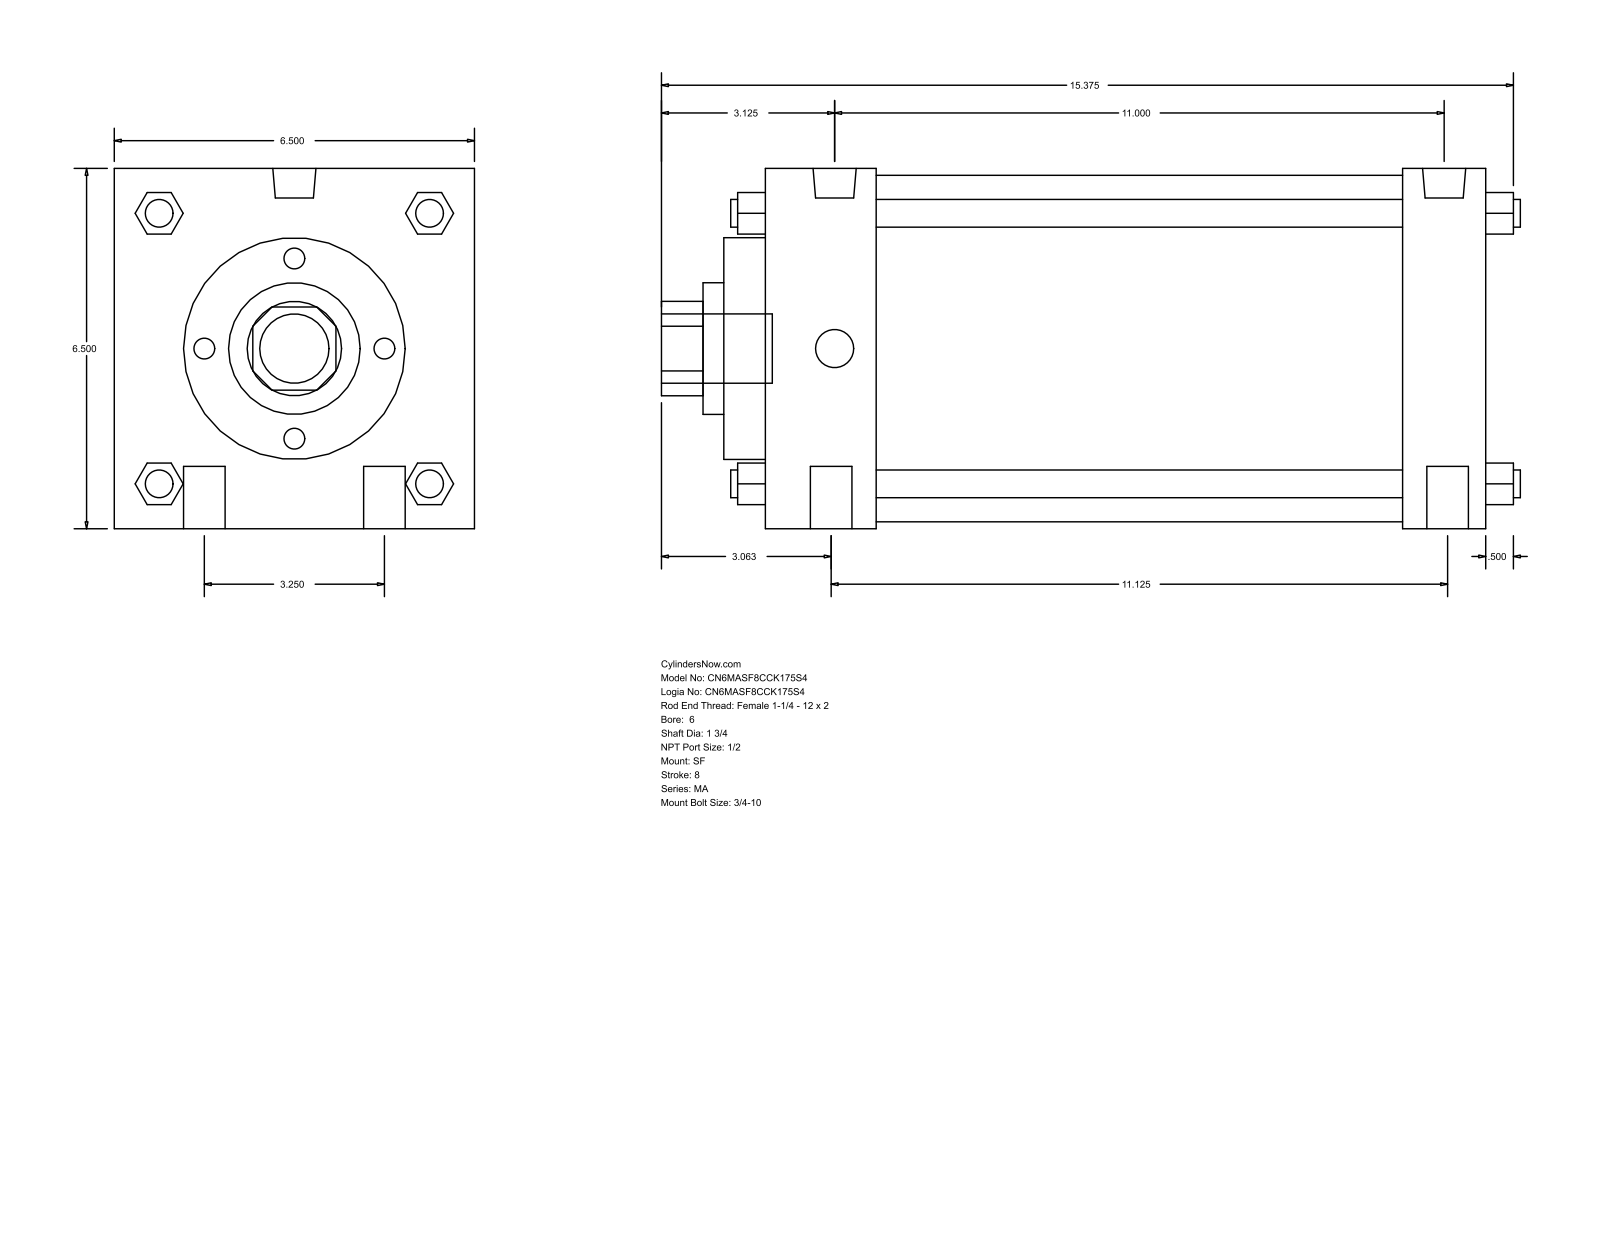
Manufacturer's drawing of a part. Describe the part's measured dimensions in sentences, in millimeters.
The part is named "MA_SF__0600_1.75". Its 3-D file was written by "GSSL Pune (CONFIG_CONTROL_DESIGN)". It is 0 solids with 126 faces: 95 planar, 31 cylindrical and 0 other. Overall it measures 393.7 by 165.1 by 165.1 millimeters. Round holes: 1 of diameter 44.45, 1 of diameter 60.33, 1 of diameter 101.6, 1 of diameter 158.75. Round bosses or shafts: 4 of diameter 19.05, 4 of diameter 12.7, 2 of diameter 19.77, 2 of diameter 17.46, 1 of diameter 31.75. Partial cylindrical surfaces (rounded edges, fillets, slot ends): 1 of radius 21.63. The main face-to-face distances are 165.1, 330.2, 19.05, 50.8, 292.11, 38.09, 241.31, 279.4, 69.85, 311.16.
